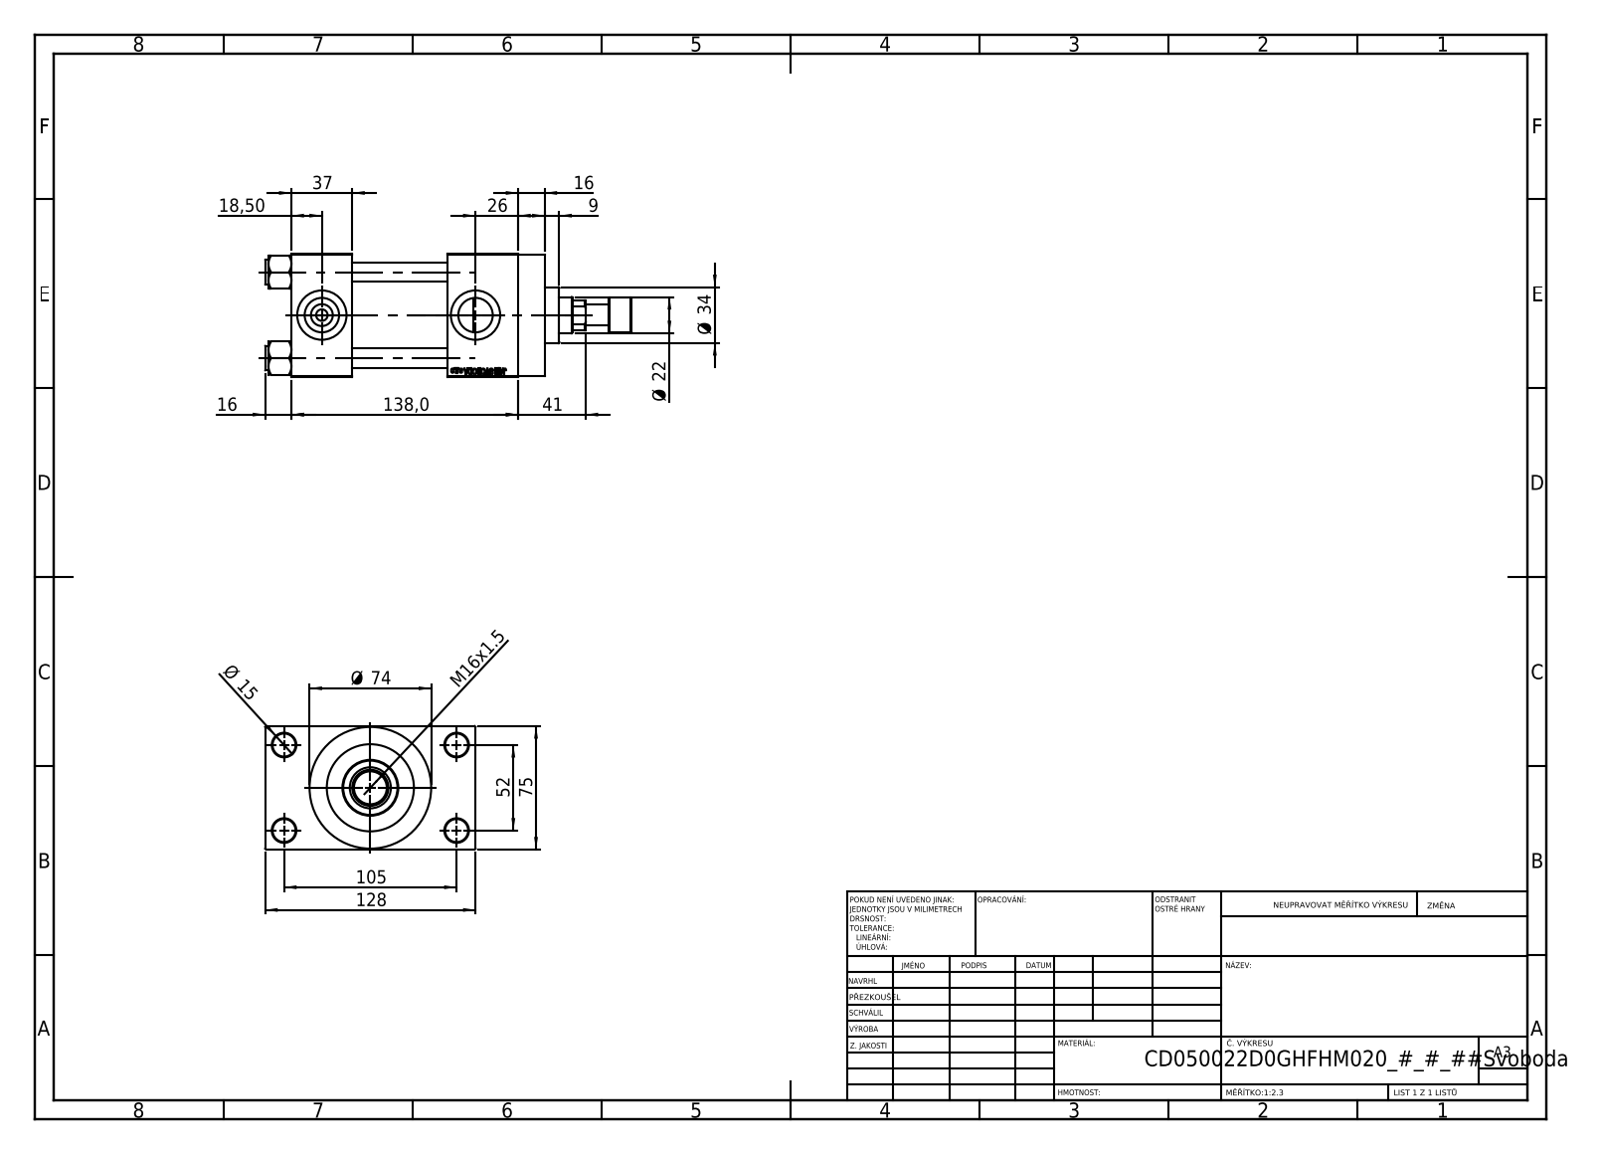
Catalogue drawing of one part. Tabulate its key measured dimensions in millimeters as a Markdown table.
| quantity | value |
| --- | --- |
| part name | V215CD_D_Body; V215CD_NUT_M5_D; V215CD_VC_A; V215CR_ROD_END_F (+2 more) |
| STEP written by | SolidWorks 2019 (CONFIG_CONTROL_DESIGN) |
| units | millimeters |
| bodies | 12 solids, 1114 faces (500 planar, 92 cylindrical, 522 other) |
| overall size | 223 × 128 × 75 |
| volume | 804 218 mm³ |
| surface area | 168 846 mm² |
| round holes (diameter × count) | 12 × 4, 14 × 4, 7 × 2, 20.96 × 2, 30 × 2, 10.5 × 1, 22 × 1, 25 × 1, 41 × 1, 50 × 1, 53 × 1 |
| round bosses / shafts (diameter × count) | 15 × 4, 74 × 1, 56 × 1, 34 × 1, 21 × 1, 13 × 1 |
| main face-to-face distances | 75, 58, 37, 95, 26.5, 138, 101, 43, 101.5, 16 |
| hole center spacings | 26.35, 36.98, 52.3, 58.43, 58.59, 78.65, 94.37, 52 |
